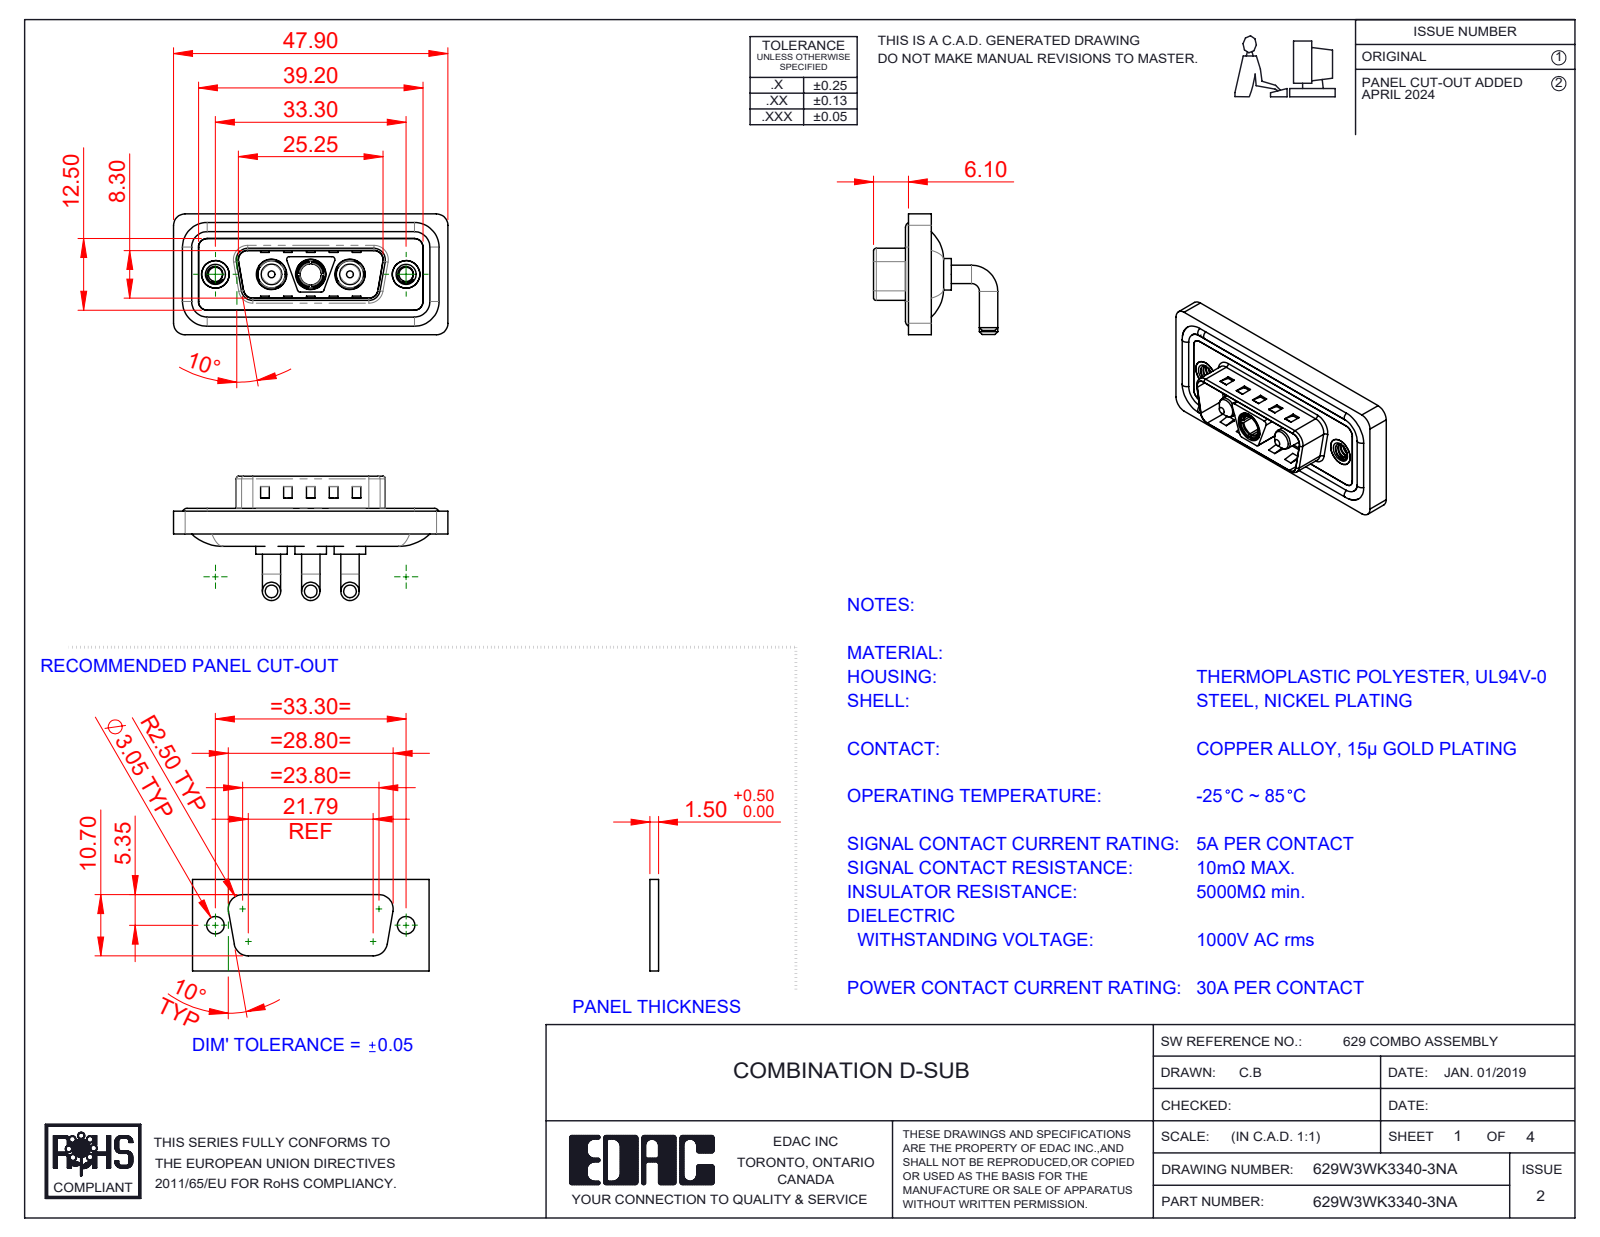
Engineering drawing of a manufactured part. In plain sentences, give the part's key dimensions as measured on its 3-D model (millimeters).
The part is named "629W3WK3340-3NA; 629Combo Waterproof Housing_15 Contacts; Power Socket_30A RA; 629Combo Threaded Rivet_A (+4 more)". Its 3-D file was written by "SolidWorks 2023 (CONFIG_CONTROL_DESIGN)". It is 13 solids with 615 faces: 231 planar, 254 cylindrical and 130 other. Overall it measures 47.9 by 21.7 by 21.1 millimeters. Its volume is 5 974 cubic millimeters and its surface area 9 476 square millimeters. Round holes: 3 of diameter 4.85, 3 of diameter 5.3, 2 of diameter 2.5, 2 of diameter 4, 2 of diameter 4.8, 2 of diameter 5, 1 of diameter 3.7. Round bosses or shafts: 6 of diameter 3.2, 4 of diameter 1.6, 3 of diameter 5.5, 3 of diameter 5.2, 3 of diameter 4.75, 3 of diameter 3.75, 2 of diameter 4.9, 2 of diameter 3.6. Partial cylindrical surfaces (rounded edges, fillets, slot ends): 20 of radius 2, 18 of radius 1.5, 12 of radius 0.5, 8 of radius 1.6, 4 of radius 0.25, 4 of radius 0.6, 4 of radius 0.65, 4 of radius 0.9. The main face-to-face distances are 0.4, 2.9, 0.8, 1.1, 2.1, 1.6, 4.5, 3.1, 2.5, 3.7. The hole center spacings are 6.85, 9.8, 16.65, 23.5, 13.7, 33.3.
